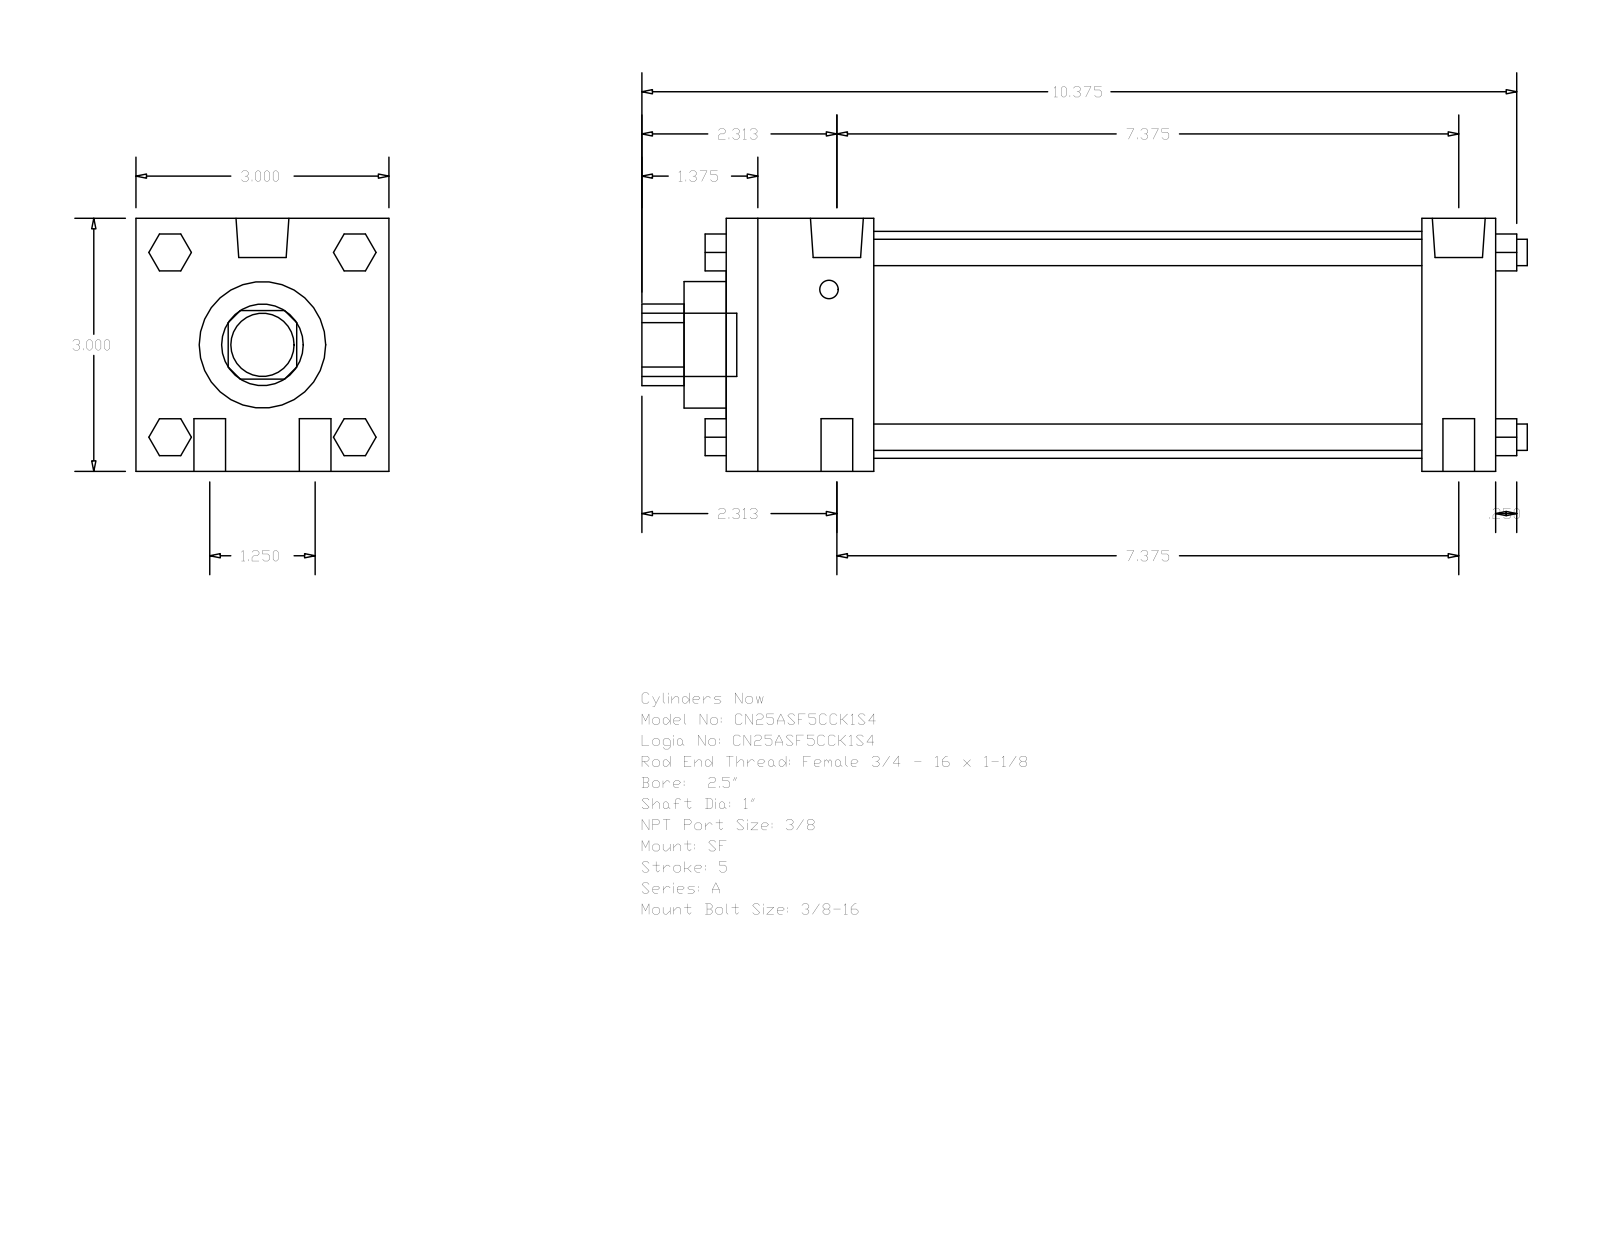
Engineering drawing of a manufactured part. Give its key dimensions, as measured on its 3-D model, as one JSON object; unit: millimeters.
{"part_name": "A_SF__0250_1", "step_written_by": "GSSL Pune (CONFIG_CONTROL_DESIGN)", "units": "millimeters", "bodies": {"solids": 0, "faces": 124, "planar": 94, "cylindrical": 30, "other": 0}, "overall_size": [266.7, 76.2, 76.2], "round_holes": [[25.4, 1], [38.1, 1], [68.33, 1]], "round_bosses_or_shafts": [[9.53, 4], [7.94, 4], [15.93, 2], [5.56, 2], [19.05, 1]], "partial_cylinders_radius": [[12.29, 1]], "face_to_face_distances": [76.2, 231.78, 209.55, 22.23, 44.45, 165.1, 187.33, 12.7, 11.11, 57.15]}
